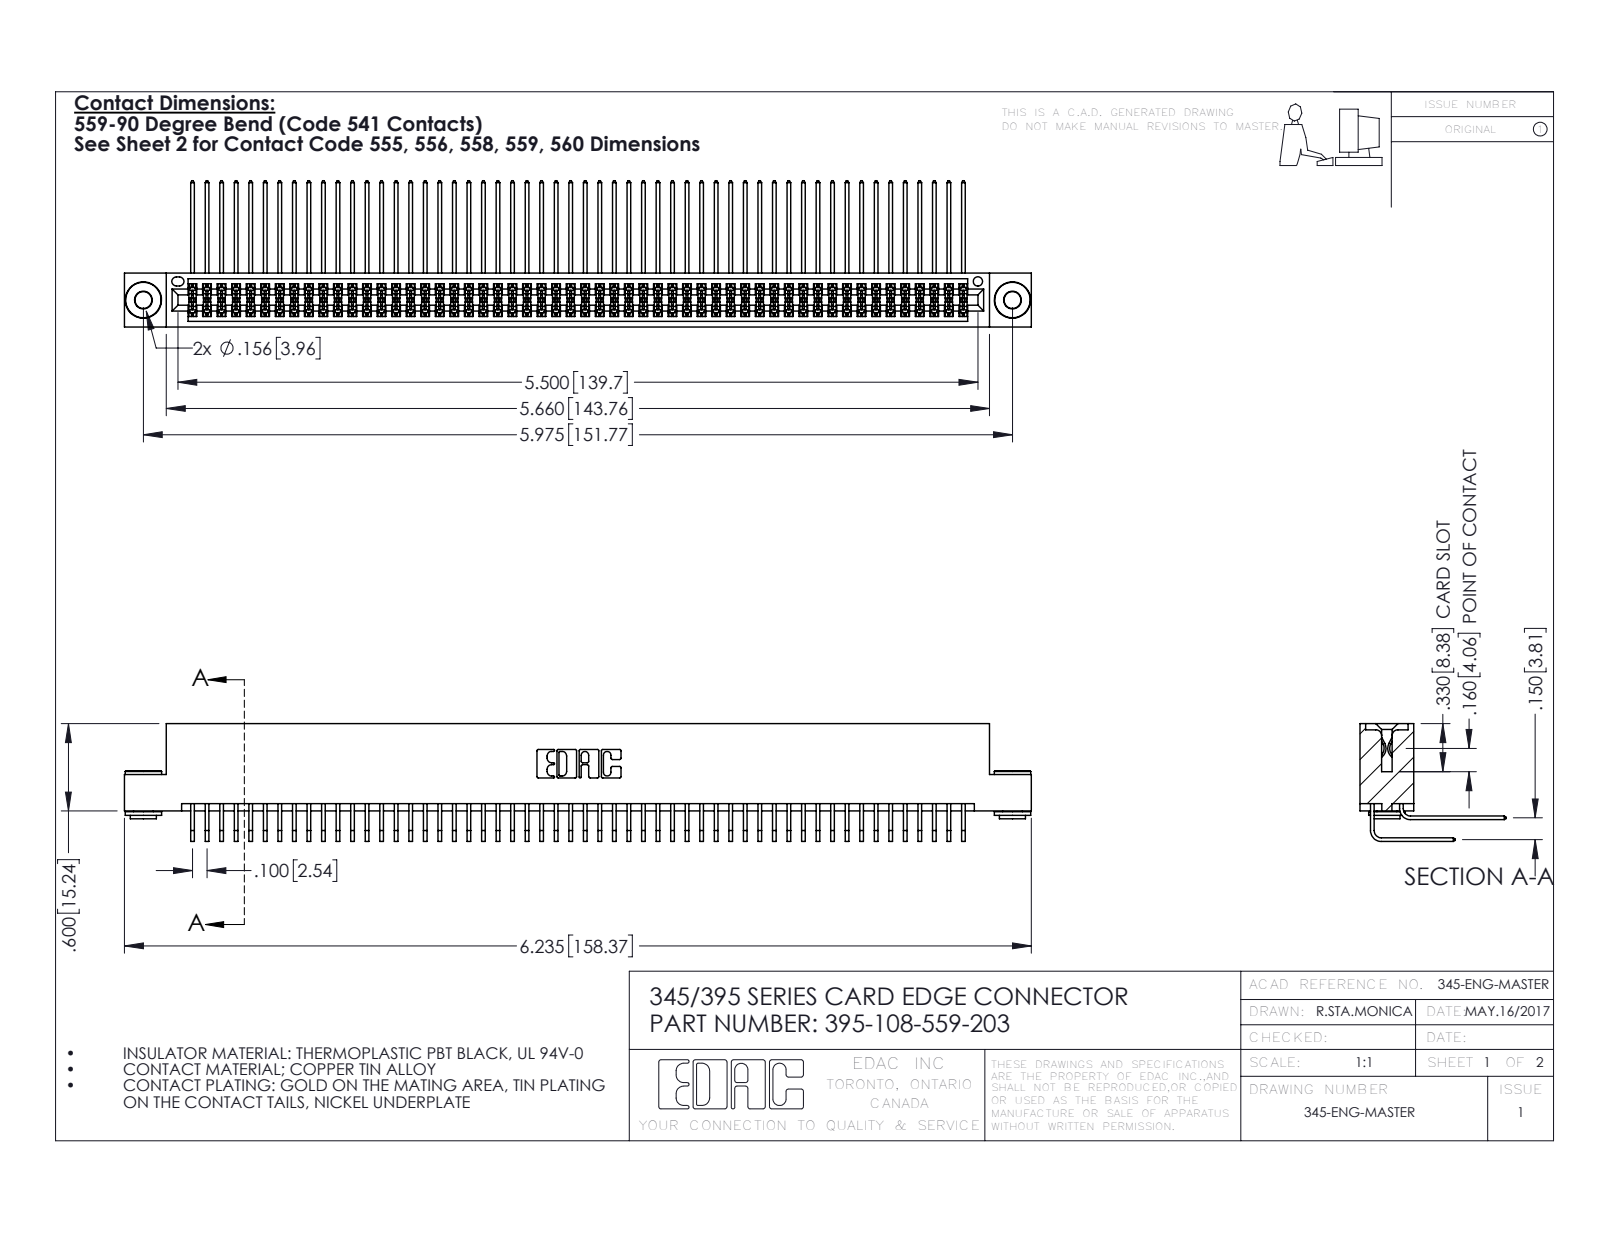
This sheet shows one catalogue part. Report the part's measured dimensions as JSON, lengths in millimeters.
{"part_name": "345-250-002_345-250-002-102; 345 Part_Flush Mounting Lugs - 0.156 Dia-TH; 345-292-001_559 Tail - 2; 345-292-001_558 559 Tail - 1 (+1 more)", "step_written_by": "SolidWorks 2016 (CONFIG_CONTROL_DESIGN)", "units": "millimeters", "bodies": {"solids": 111, "faces": 5780, "planar": 3870, "cylindrical": 1902, "other": 8}, "overall_size": [158.4, 25.5, 20.5], "volume_mm3": 16100, "surface_area_mm2": 27220, "round_holes": [[2.9, 2], [4, 2], [1.6, 1]], "round_bosses_or_shafts": [[6.4, 2], [4.6, 2], [3.5, 2]], "partial_cylinders_radius": [[0.2, 162], [0.3, 22], [0.2, 6], [0.8, 6], [0.7, 3], [0.4, 2], [0.5, 2], [0.6, 2]], "face_to_face_distances": [1.8, 7.6, 5.1, 9.4, 0.6, 2.5, 6.9, 5.7, 4.4, 3.8], "hole_center_spacings": [6.9, 145.8, 151.8]}
